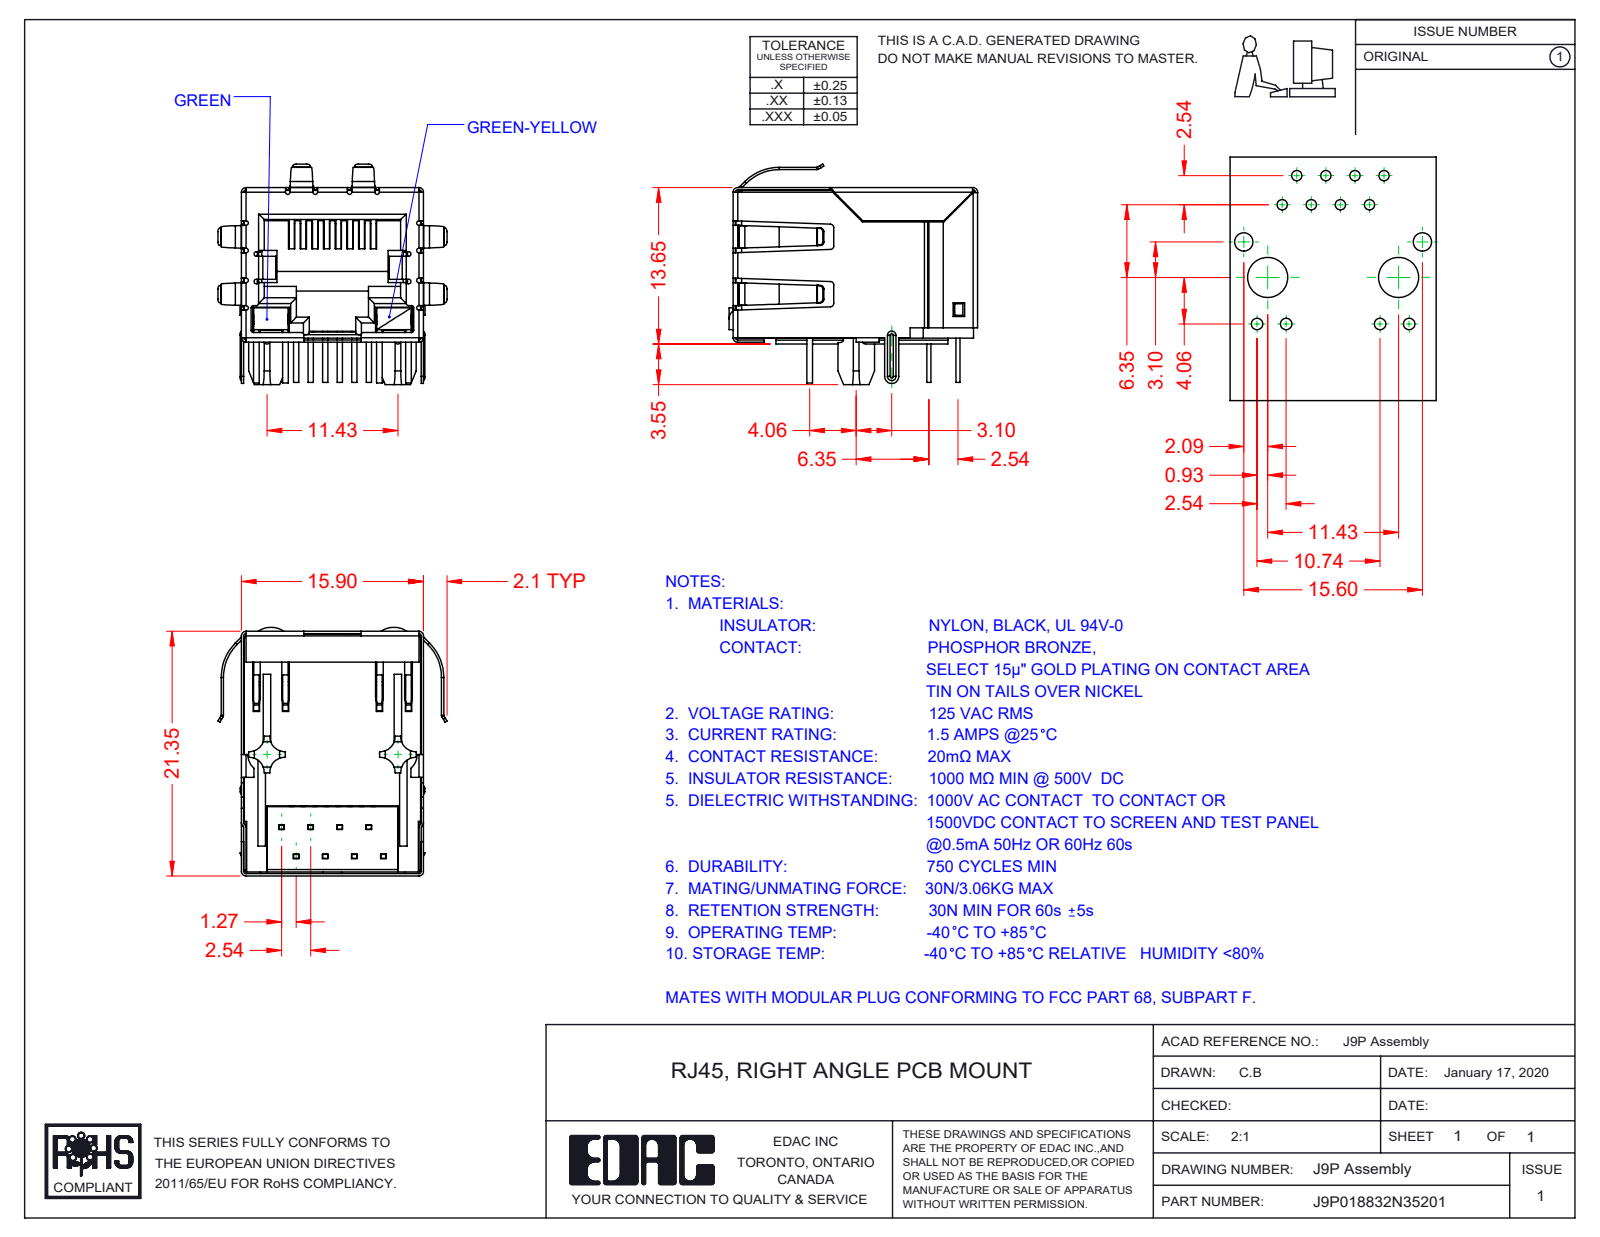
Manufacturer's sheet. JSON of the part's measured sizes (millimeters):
{"part_name": "9P-LED LED LH_3-Green; 9P-LED Assembly; 9P-LED Contacts; J9P018832N35202 (+4 more)", "step_written_by": "SolidWorks 2016 (CONFIG_CONTROL_DESIGN)", "units": "millimeters", "bodies": {"solids": 13, "faces": 1474, "planar": 1042, "cylindrical": 338, "other": 94}, "overall_size": [21.7, 20, 19.25], "volume_mm3": 2687, "surface_area_mm2": 7515, "partial_cylinders_radius": [[0.2, 39], [0.5, 22], [0.3, 20], [0.4, 16], [1.3, 8], [0.23, 5], [0.11, 4], [0.31, 4]], "face_to_face_distances": [15.45, 15.7, 15.65, 0.35, 0.54, 15.5, 12.36, 0.6, 1.4, 0.59]}
